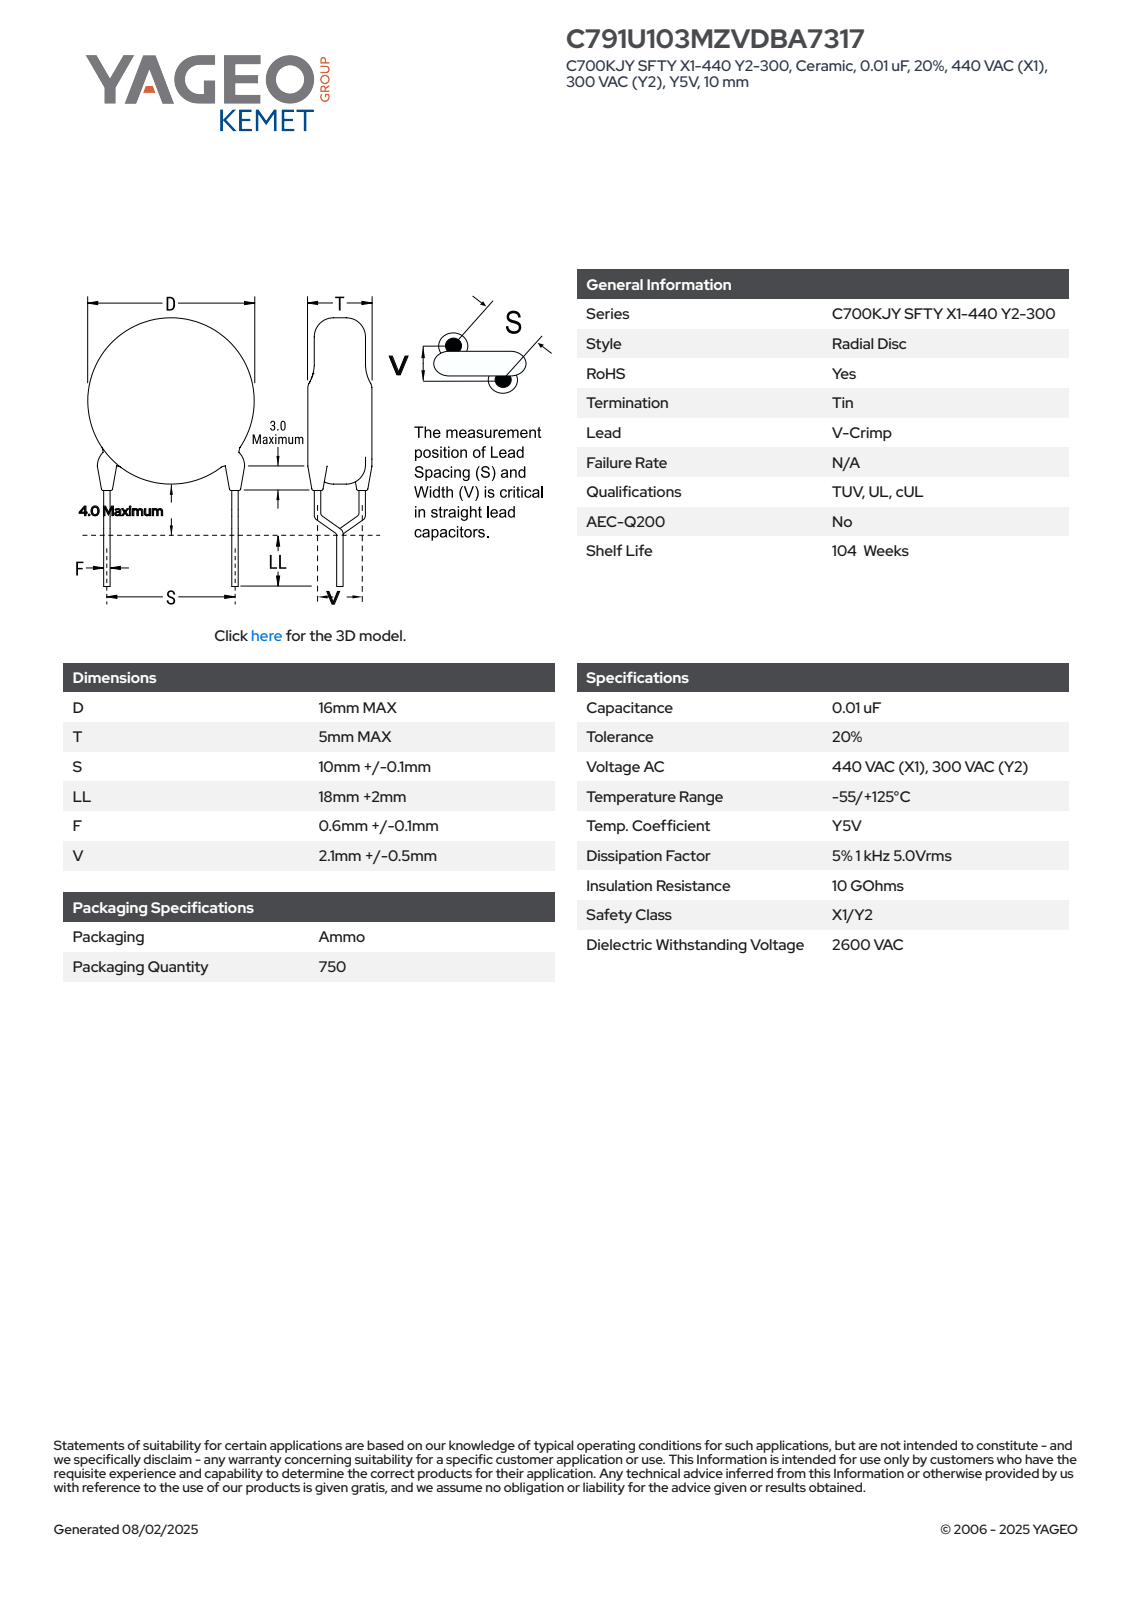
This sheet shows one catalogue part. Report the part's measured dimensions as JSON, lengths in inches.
{"part_name": "CCD_VC16X5_D16T5S10LL20F0.7V2.1", "step_written_by": "SolidWorks 2021 (AUTOMOTIVE_DESIGN)", "units": "inches", "bodies": {"solids": 4, "faces": 85, "planar": 63, "cylindrical": 18, "other": 4}, "overall_size": [1.417, 0.63, 0.197], "volume_in3": 0.061, "surface_area_in2": 1.14, "round_bosses_or_shafts": [[0.028, 6], [0.047, 2], [0.63, 1]], "face_to_face_distances": [0.197, 0.787, 1.152, 0.365, 1.076, 0.289, 0.076, 0.021, 0.014, 0.312]}
